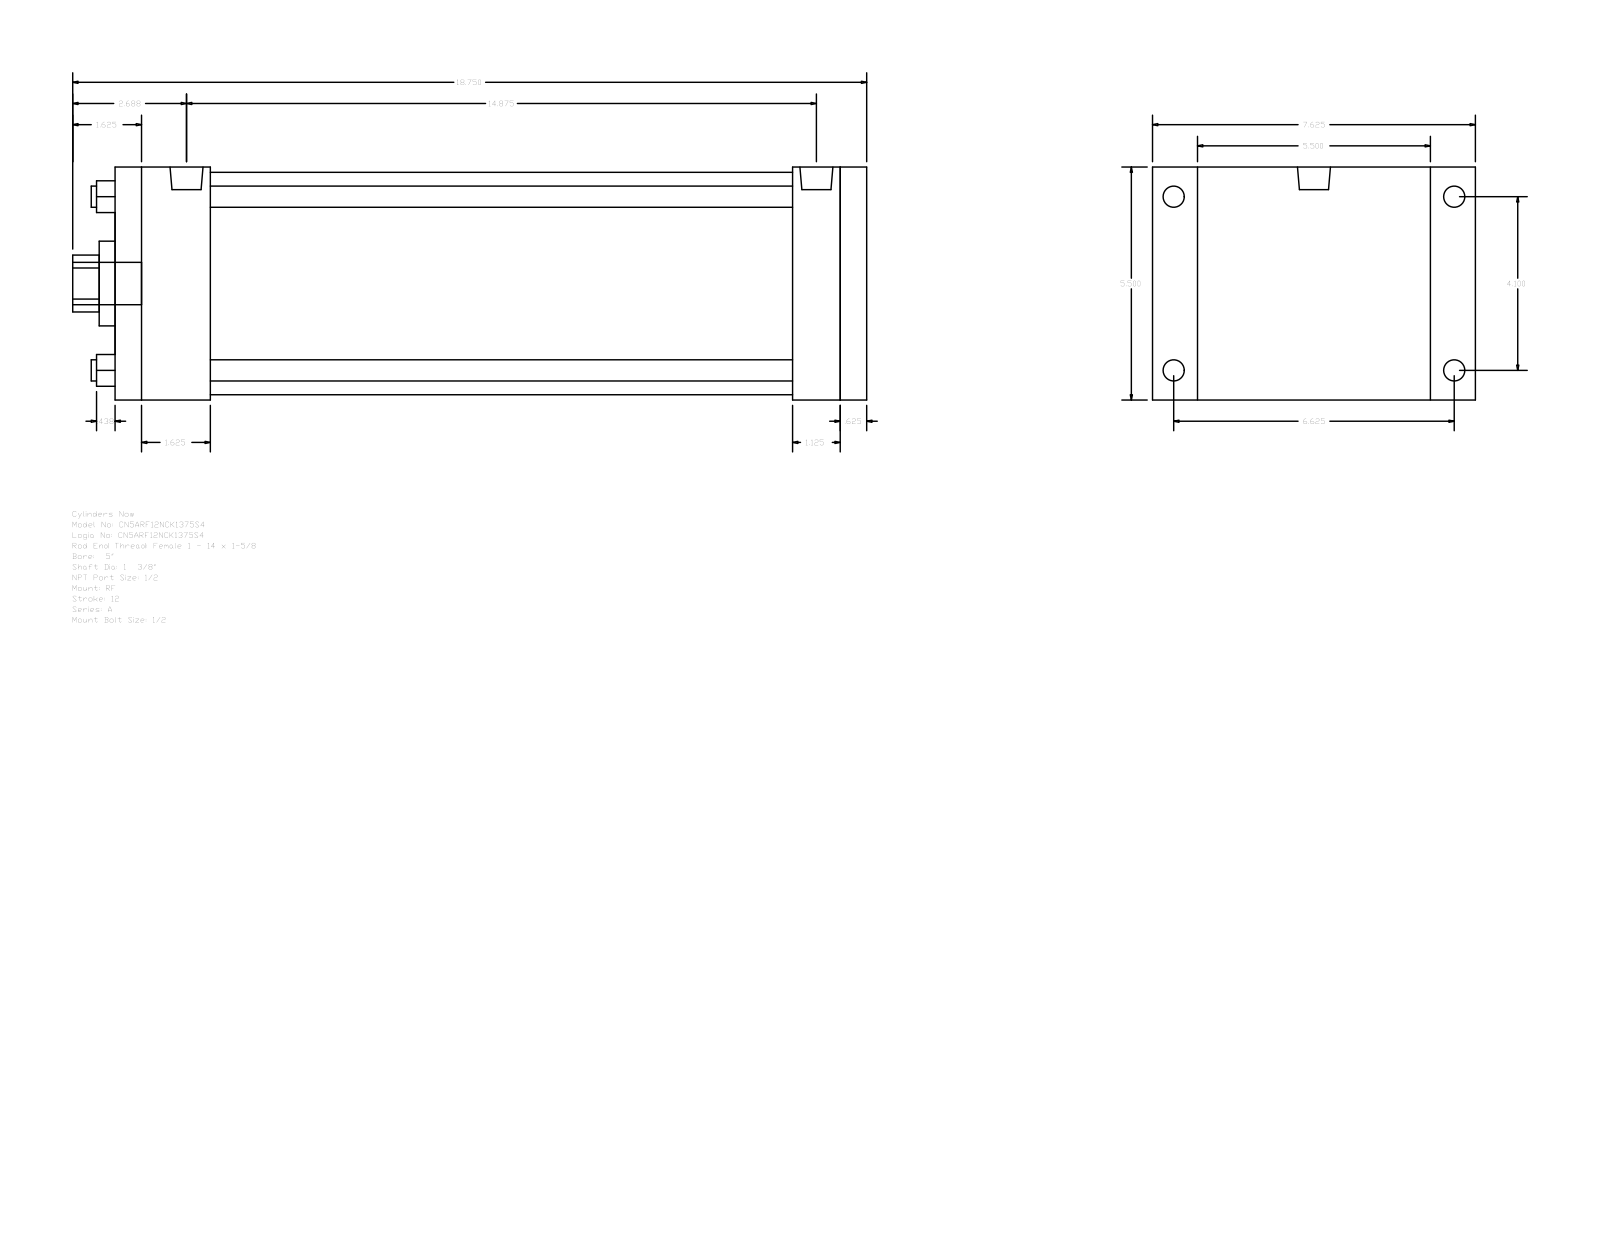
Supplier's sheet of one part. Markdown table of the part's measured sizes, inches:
| quantity | value |
| --- | --- |
| part name | A_RF__0500_1.375 |
| STEP written by | GSSL Pune (CONFIG_CONTROL_DESIGN) |
| units | inches |
| bodies | 0 solids, 92 faces (64 planar, 28 cylindrical, 0 other) |
| overall size | 18.75 × 7.625 × 5.5 |
| round holes (diameter × count) | 0.5 × 4, 1.375 × 1, 2 × 1, 5.25 × 1 |
| round bosses / shafts (diameter × count) | 0.5 × 4, 0.344 × 4, 0.778 × 2, 1 × 1 |
| partial cylindrical surfaces (radius × count) | 0.672 × 1 |
| main face-to-face distances | 5.5, 17.75, 0.625, 17.125, 1.125, 2.25, 14.875, 15.5, 16, 13.75 |
| hole center spacings | 2.899, 4.1, 5.798 |
